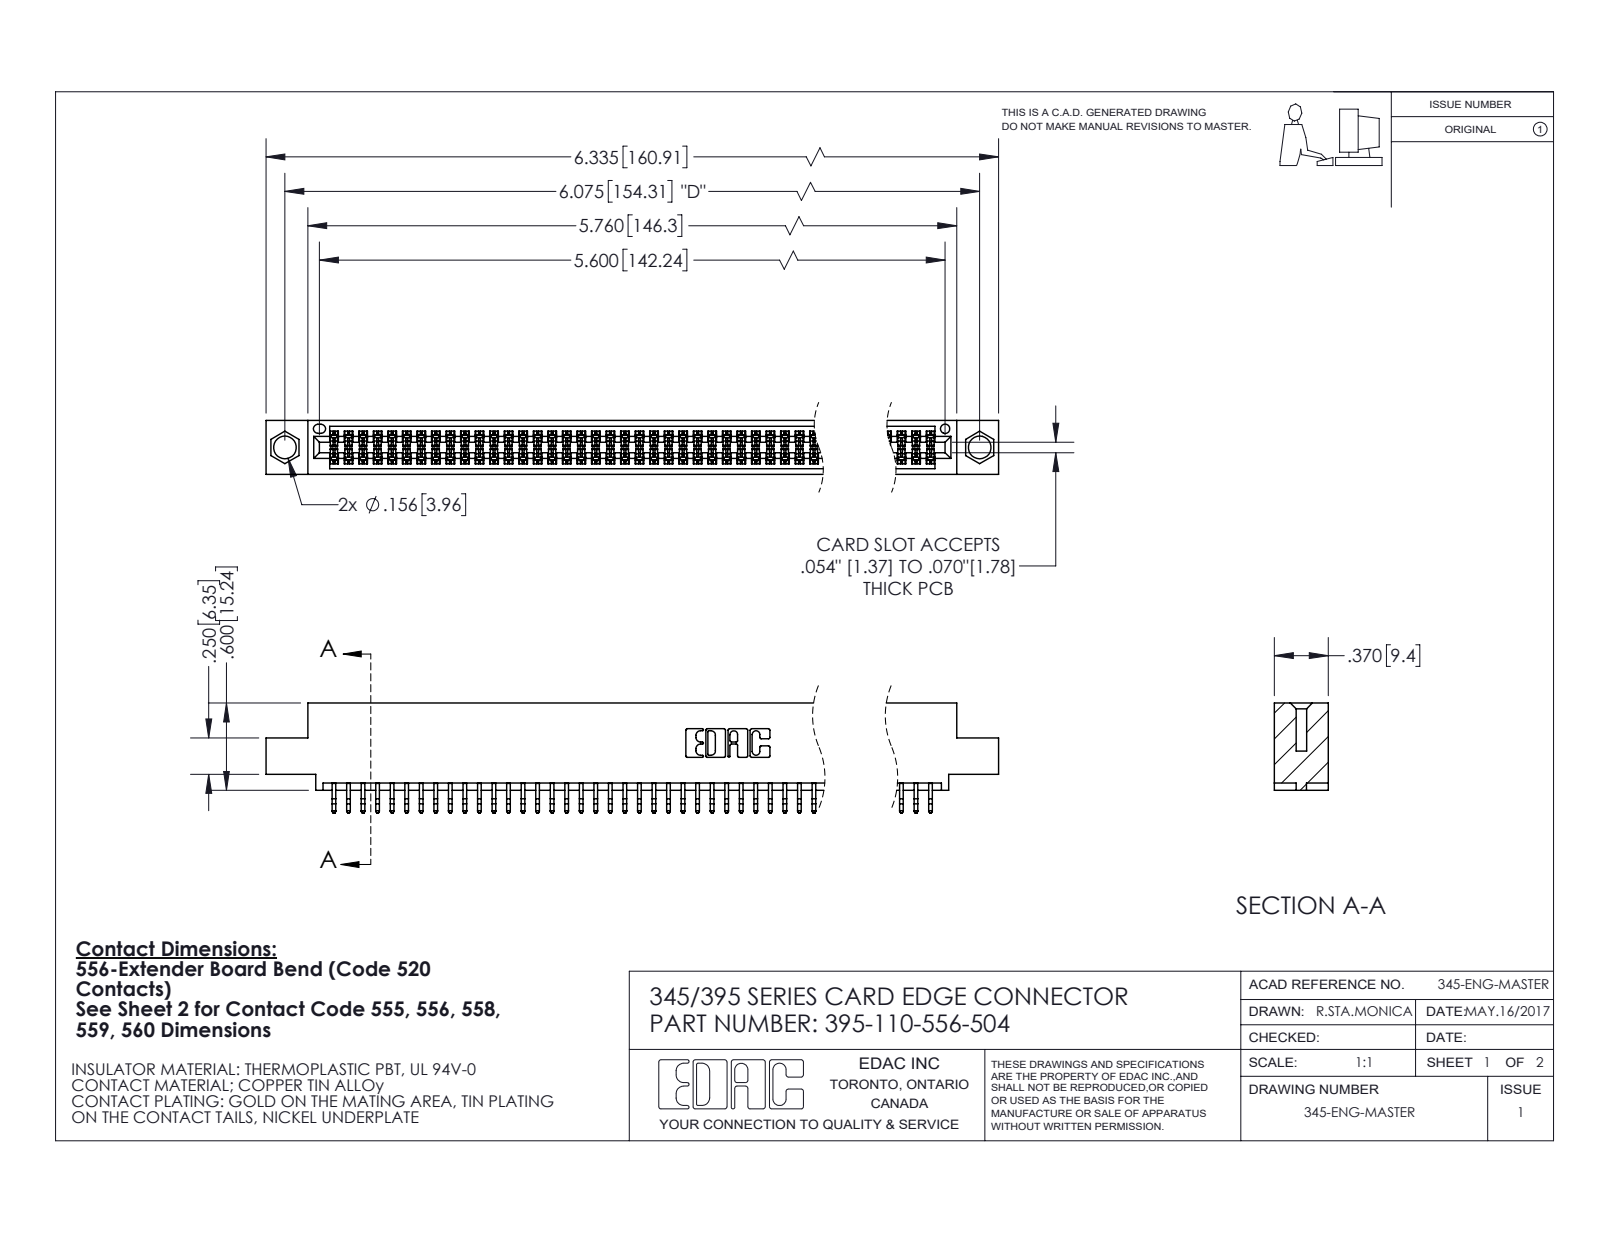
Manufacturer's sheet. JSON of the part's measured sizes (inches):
{"part_name": "395-110-556-504; 345 Part_0.110 Offset - 0.156 Dia-TI; 345-292-001_556 Tail", "step_written_by": "SolidWorks 2020 (CONFIG_CONTROL_DESIGN)", "units": "inches", "bodies": {"solids": 111, "faces": 6304, "planar": 4168, "cylindrical": 2136, "other": 0}, "overall_size": [6.335, 0.757, 0.37], "volume_in3": 0.95, "surface_area_in2": 35.82, "round_holes": [[0.156, 2], [0.064, 1]], "partial_cylinders_radius": [[0.006, 220], [0.01, 22], [0.007, 6], [0.031, 6], [0.026, 3], [0.01, 2], [0.014, 2], [0.019, 2]], "face_to_face_distances": [0.298, 0.072, 0.37, 0.2, 0.025, 0.098, 0.272, 0.225, 0.175, 0.149], "hole_center_spacings": [0.27, 5.839, 6.075]}
